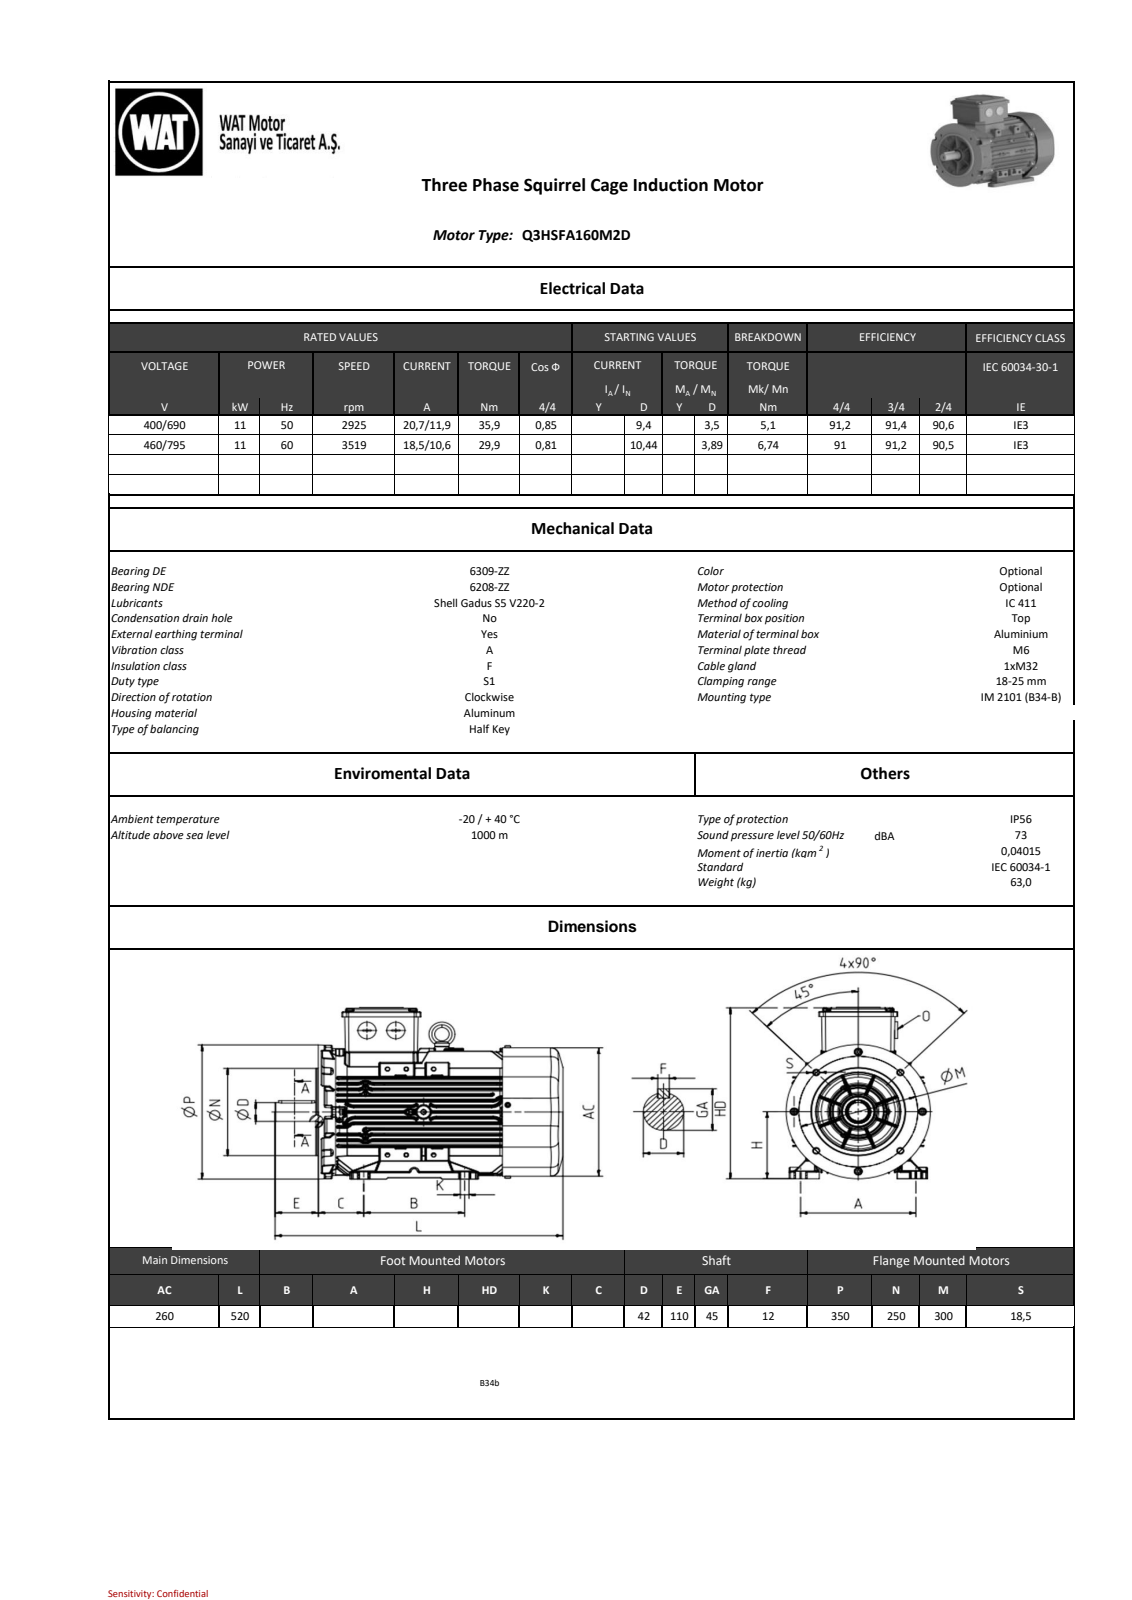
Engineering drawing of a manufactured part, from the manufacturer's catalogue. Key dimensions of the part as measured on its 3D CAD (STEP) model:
Part name (STEP PRODUCT): QHS series_ 160_B5_stp_objects
STEP written by: SIEMENS PLM Software NX2206.8101 (AP203_CONFIGURATION_CONTROLLED_3D_DESIGN_OF_MECHANICAL_PARTS_AND_ASSEMBLIES_MIM_LF)
Units: millimetres
Bodies: 0 solids, 5987 faces (1434 planar, 2677 cylindrical, 1876 other)
Overall size (bounding box): 519.49 × 374.4 × 349.89
Round holes (diameter × count): ⌀17 ×5, ⌀5.5 ×4, ⌀6.8 ×2, ⌀8 ×2, ⌀8.47 ×2, ⌀8.48 ×1, ⌀8.48 ×1, ⌀8.57 ×1, ⌀8.61 ×1, ⌀16 ×1, ⌀62 ×1, ⌀68.67 ×1
Round bosses / shafts (diameter × count): ⌀8 ×3, ⌀38 ×2, ⌀13 ×2, ⌀250 ×1, ⌀230.5 ×1, ⌀86.77 ×1, ⌀45 ×1, ⌀42 ×1
Partial cylindrical surfaces — rounded edges, fillets, slot ends (radius × count): R0.8 ×870, R1 ×622, R3 ×68, R2 ×52, R7 ×48, R1.5 ×32, R0.5 ×18, R5 ×18
Main face-to-face distances: 1.5, 10.42, 10.56, 20.84, 10.28, 7, 14, 125.58, 84.04, 115.18
Hole centre spacings: 74.95, 106, 120.5, 170.41, 125, 149.91, 178.91, 241
